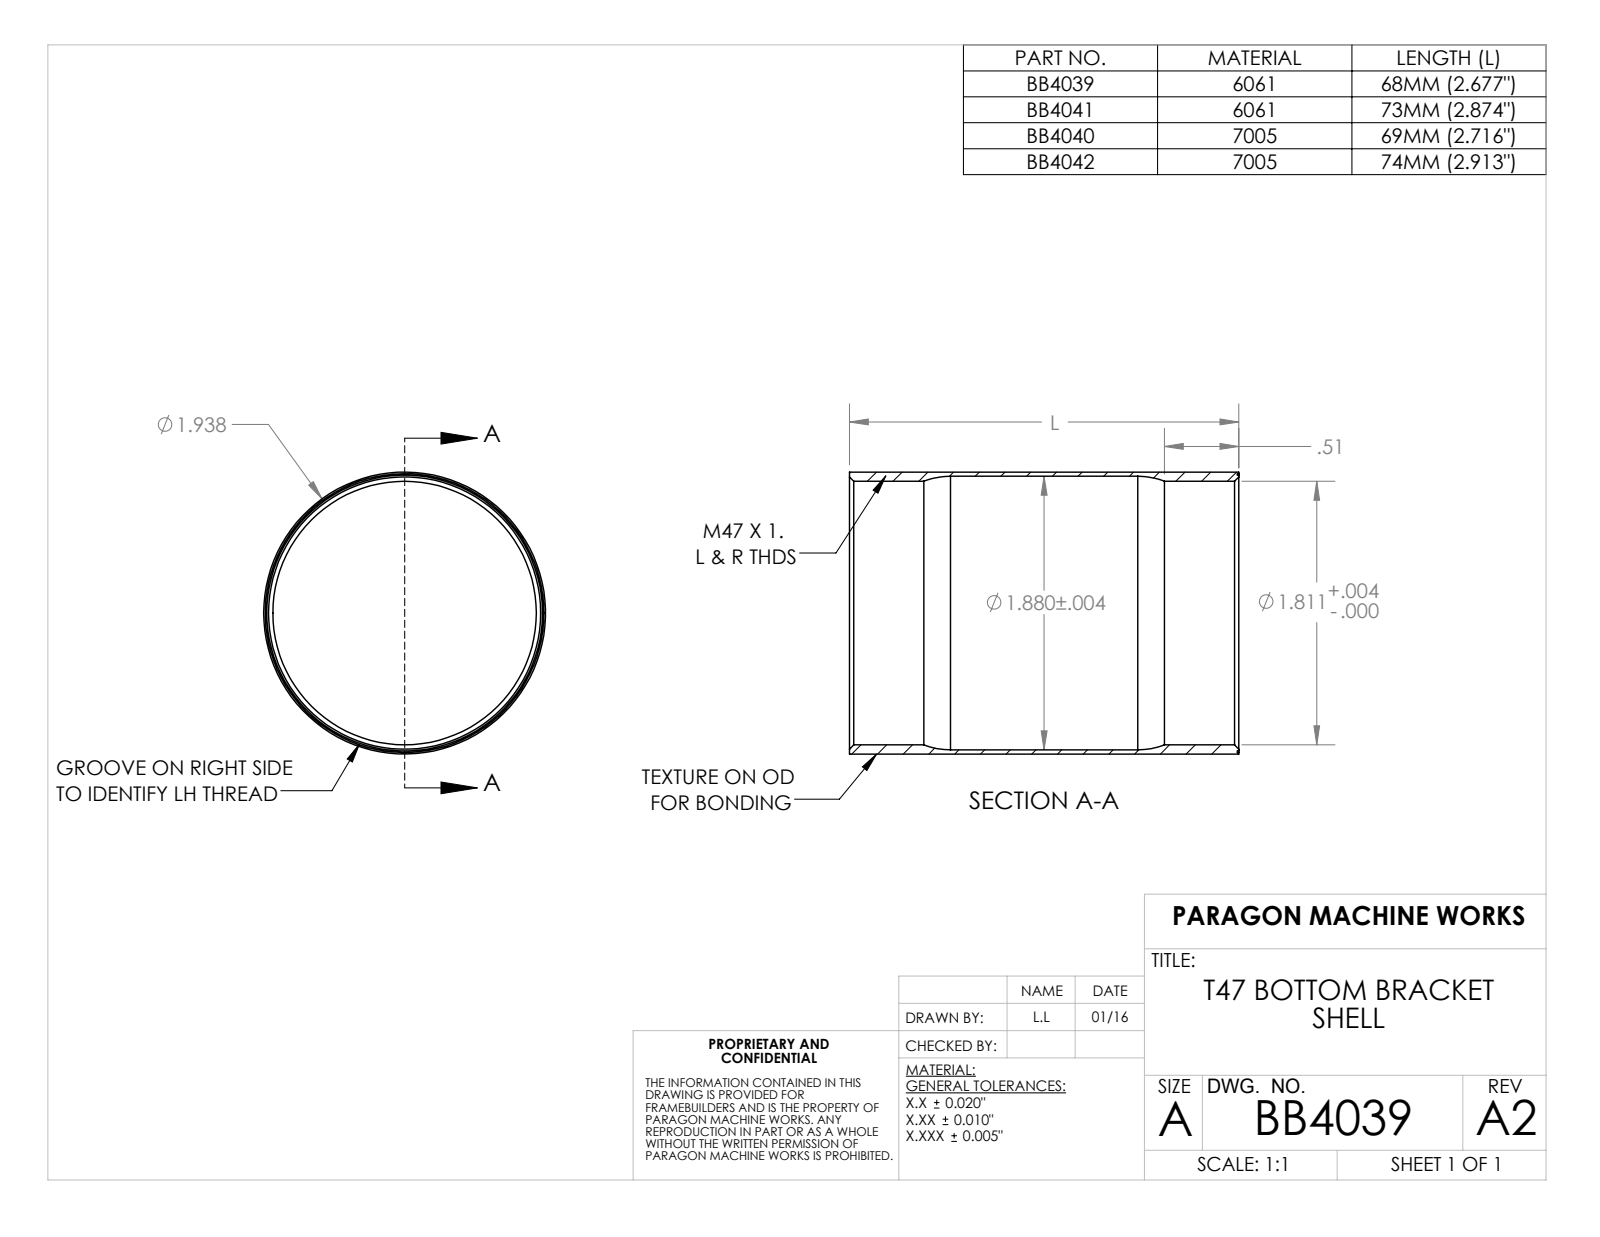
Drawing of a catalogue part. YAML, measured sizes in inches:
part_name: "BB4039"
step_written_by: "SolidWorks 2016 (AUTOMOTIVE_DESIGN)"
units: inches
bodies: {solids: 1, faces: 24, planar: 4, cylindrical: 12, other: 8}
overall_size: [2.677, 1.937, 1.937]
volume: 0.685
surface_area: 32.57
round_holes:
  - {diameter: 1.811, count: 1}
  - {diameter: 1.88, count: 1}
  - {diameter: 1.916, count: 1}
round_bosses_or_shafts:
  - {diameter: 1.937, count: 1}
  - {diameter: 1.896, count: 1}
face_to_face_distances: [2.677, 2.667]
